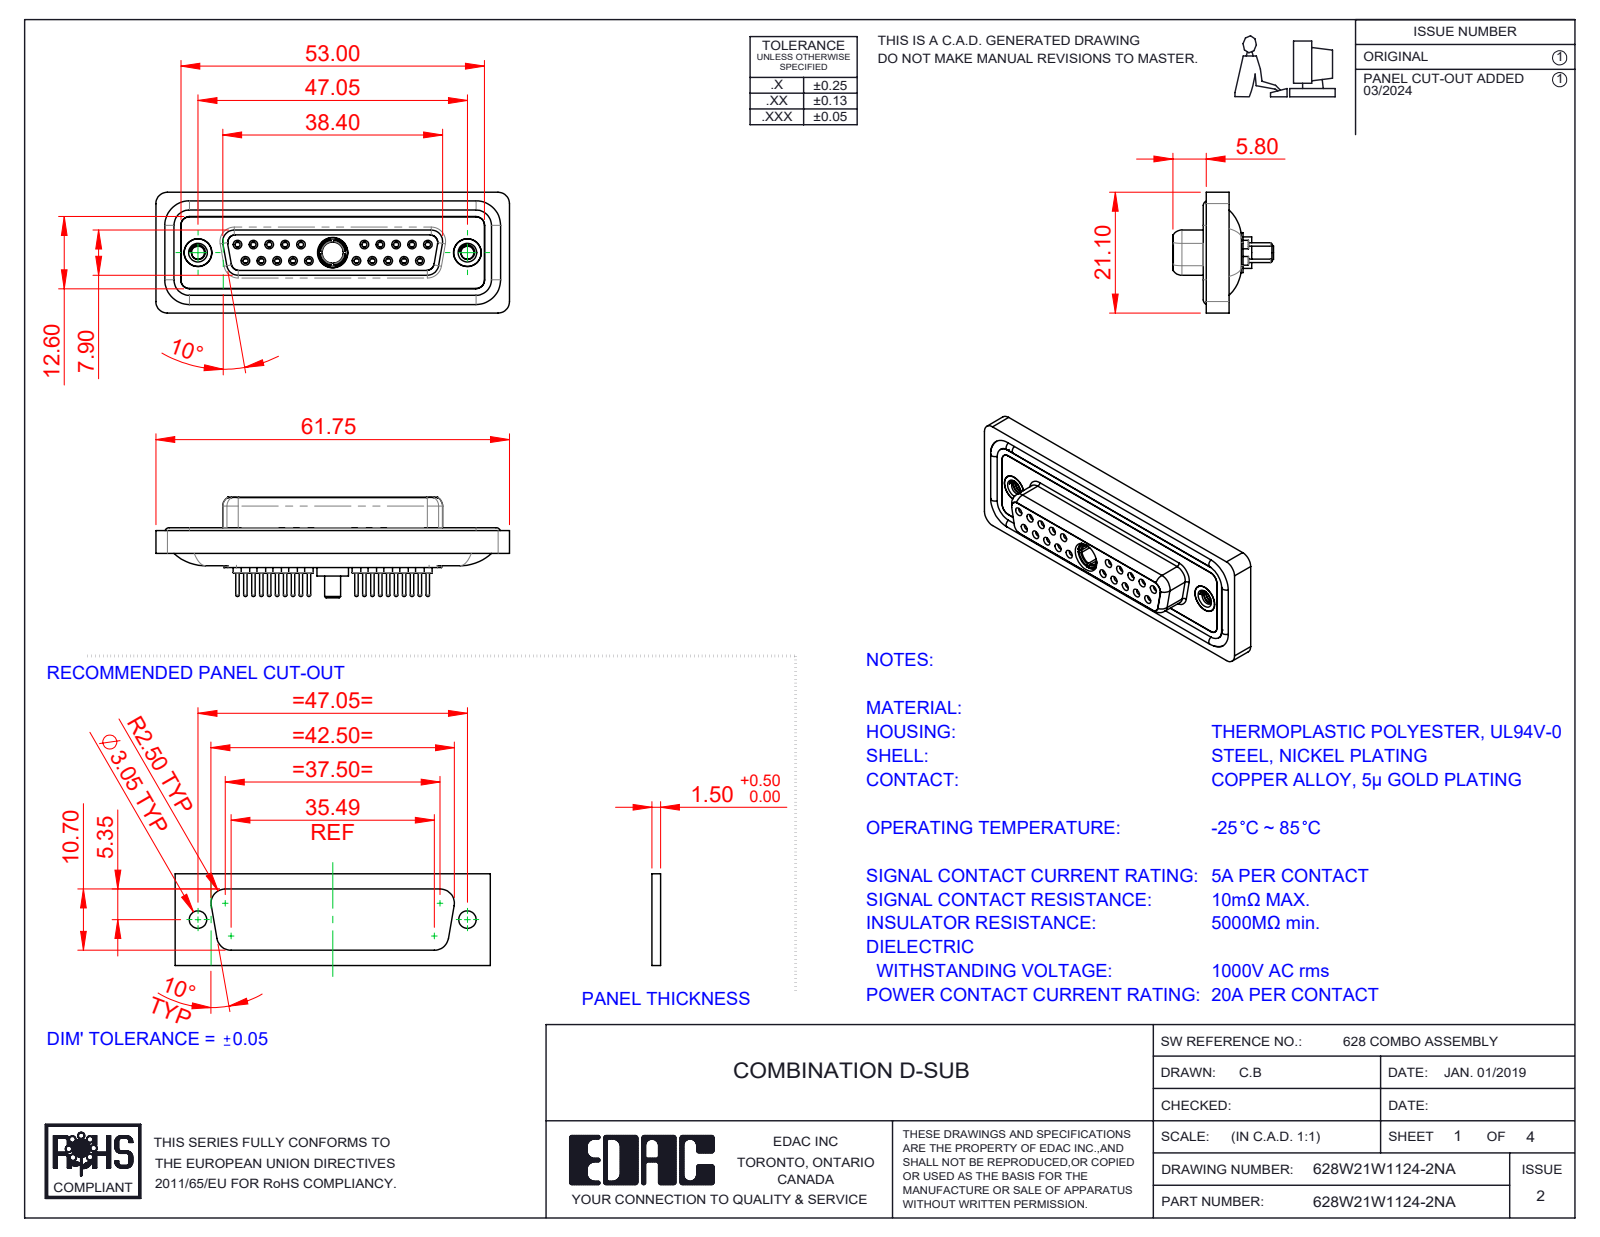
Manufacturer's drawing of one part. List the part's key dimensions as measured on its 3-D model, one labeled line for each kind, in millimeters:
Part name (STEP PRODUCT): 628Combo Threaded Rivet_A; 628W21W1124-2NA; 628Combo Housing_21W1; 628Combo Contact Row 1_24 (+5 more)
STEP written by: SolidWorks 2023 (CONFIG_CONTROL_DESIGN)
Units: millimetres
Bodies: 29 solids, 1558 faces (434 planar, 593 cylindrical, 531 other)
Overall size (bounding box): 61.75 × 21.1 × 17.55
Volume: 8 376 mm³ · Surface area: 13 999 mm²
Round holes (diameter × count): ⌀0.9 ×20, ⌀1.1 ×20, ⌀1.5 ×20, ⌀2 ×20, ⌀1.6 ×10, ⌀1.7 ×10, ⌀4.85 ×3, ⌀2.26 ×2, ⌀4 ×2, ⌀4.05 ×2, ⌀5 ×2, ⌀3.7 ×1
Round bosses / shafts (diameter × count): ⌀2.2 ×20, ⌀0.6 ×20, ⌀1.6 ×14, ⌀4.95 ×2, ⌀4.8 ×2, ⌀5.5 ×1, ⌀5.2 ×1, ⌀4.96 ×1
Partial cylindrical surfaces — rounded edges, fillets, slot ends (radius × count): R1.5 ×22, R2 ×18, R1.35 ×8, R1.6 ×8, R0.25 ×4, R0.5 ×4, R0.6 ×4, R0.65 ×4
Main face-to-face distances: 0.4, 1.8, 7.45, 6.6, 5.65, 0.5, 1.6, 7.05, 2.9, 1.1
Hole centre spacings: 3.16, 2.77, 5.54, 5.03, 8.31, 7.48, 16.62, 19.39
